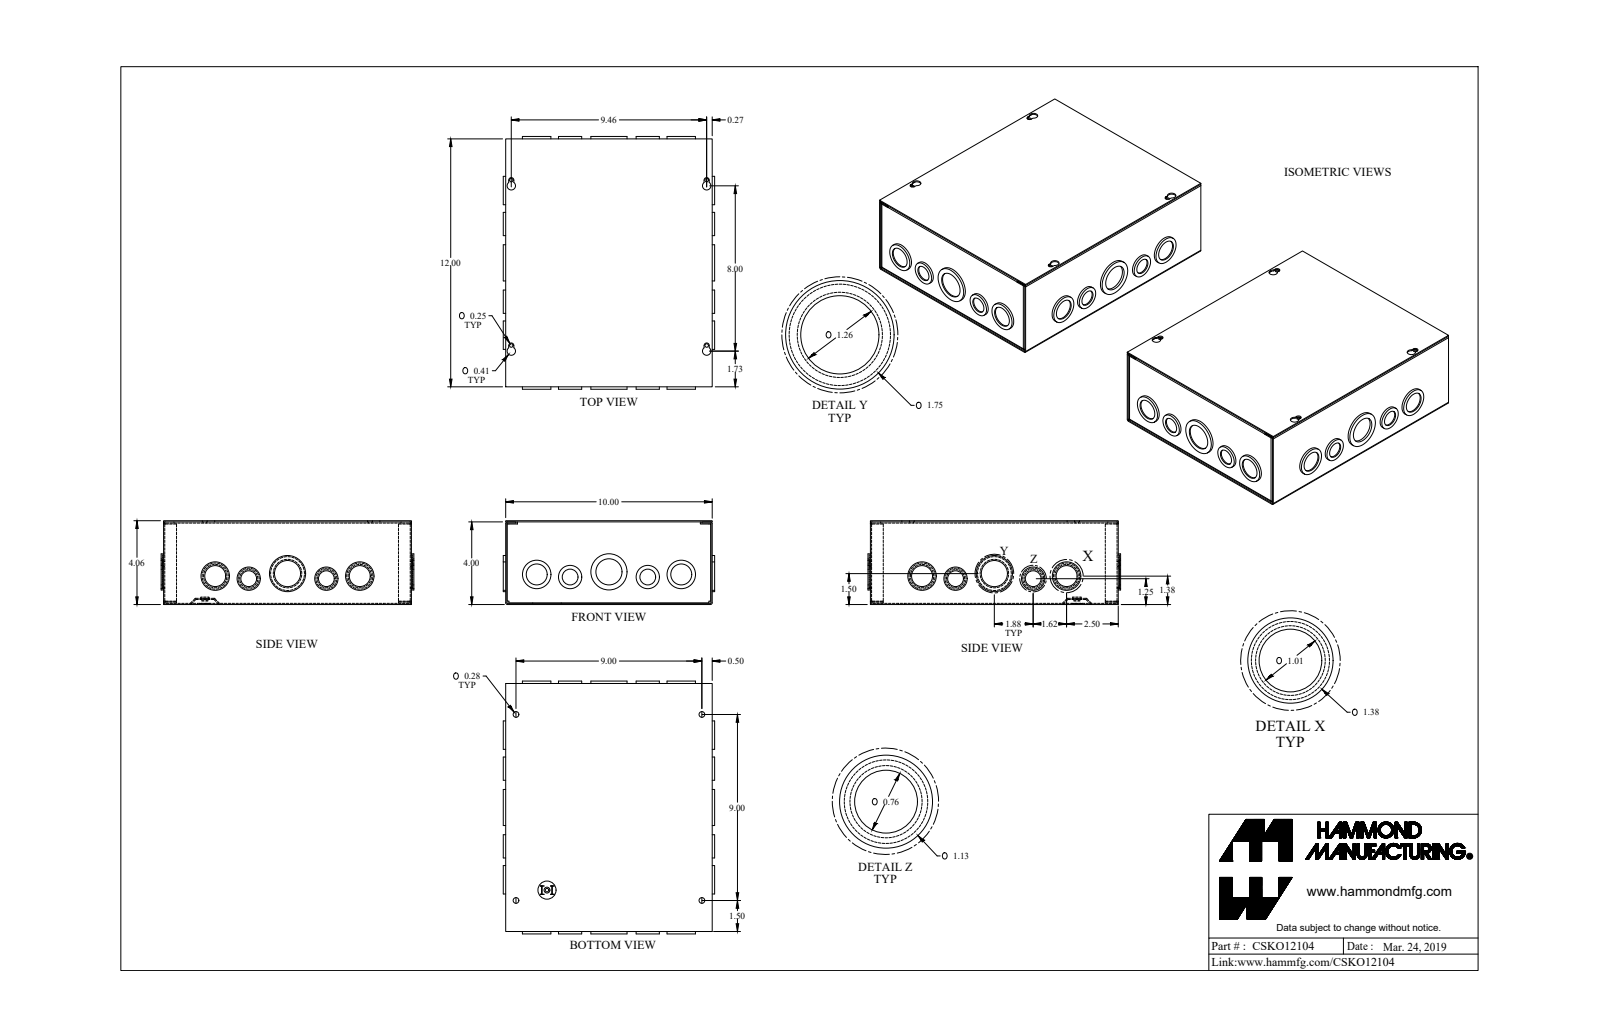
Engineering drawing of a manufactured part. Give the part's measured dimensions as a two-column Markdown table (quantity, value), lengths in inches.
| quantity | value |
| --- | --- |
| part name | CSKO12104_Default |
| STEP written by | SolidWorks 2019 (CONFIG_CONTROL_DESIGN) |
| units | inches |
| bodies | 4 solids, 445 faces (205 planar, 232 cylindrical, 8 other) |
| overall size | 12.234 × 10.234 × 4.057 |
| volume | 26.24 in³ |
| surface area | 931.3 in² |
| round holes (diameter × count) | 1.011 × 8, 1.261 × 6, 0.17 × 5, 0.281 × 4, 0.761 × 4, 1.636 × 2, 0.5 × 1 |
| round bosses / shafts (diameter × count) | 1.125 × 6, 1.375 × 5, 0.875 × 4, 1.75 × 2, 1.125 × 2, 0.875 × 2, 1.375 × 1, 0.492 × 1 |
| partial cylindrical surfaces (radius × count) | 0.029 × 12, 0.086 × 12, 0.057 × 8, 0.125 × 4, 0.203 × 4 |
| main face-to-face distances | 0.057, 4, 3.943, 4.057, 9.943, 11.943, 10, 12, 9.886, 11.886 |
| hole center spacings | 0.55, 1.625, 1.896, 3.502, 5.381, 8.503, 9, 9.243 |
